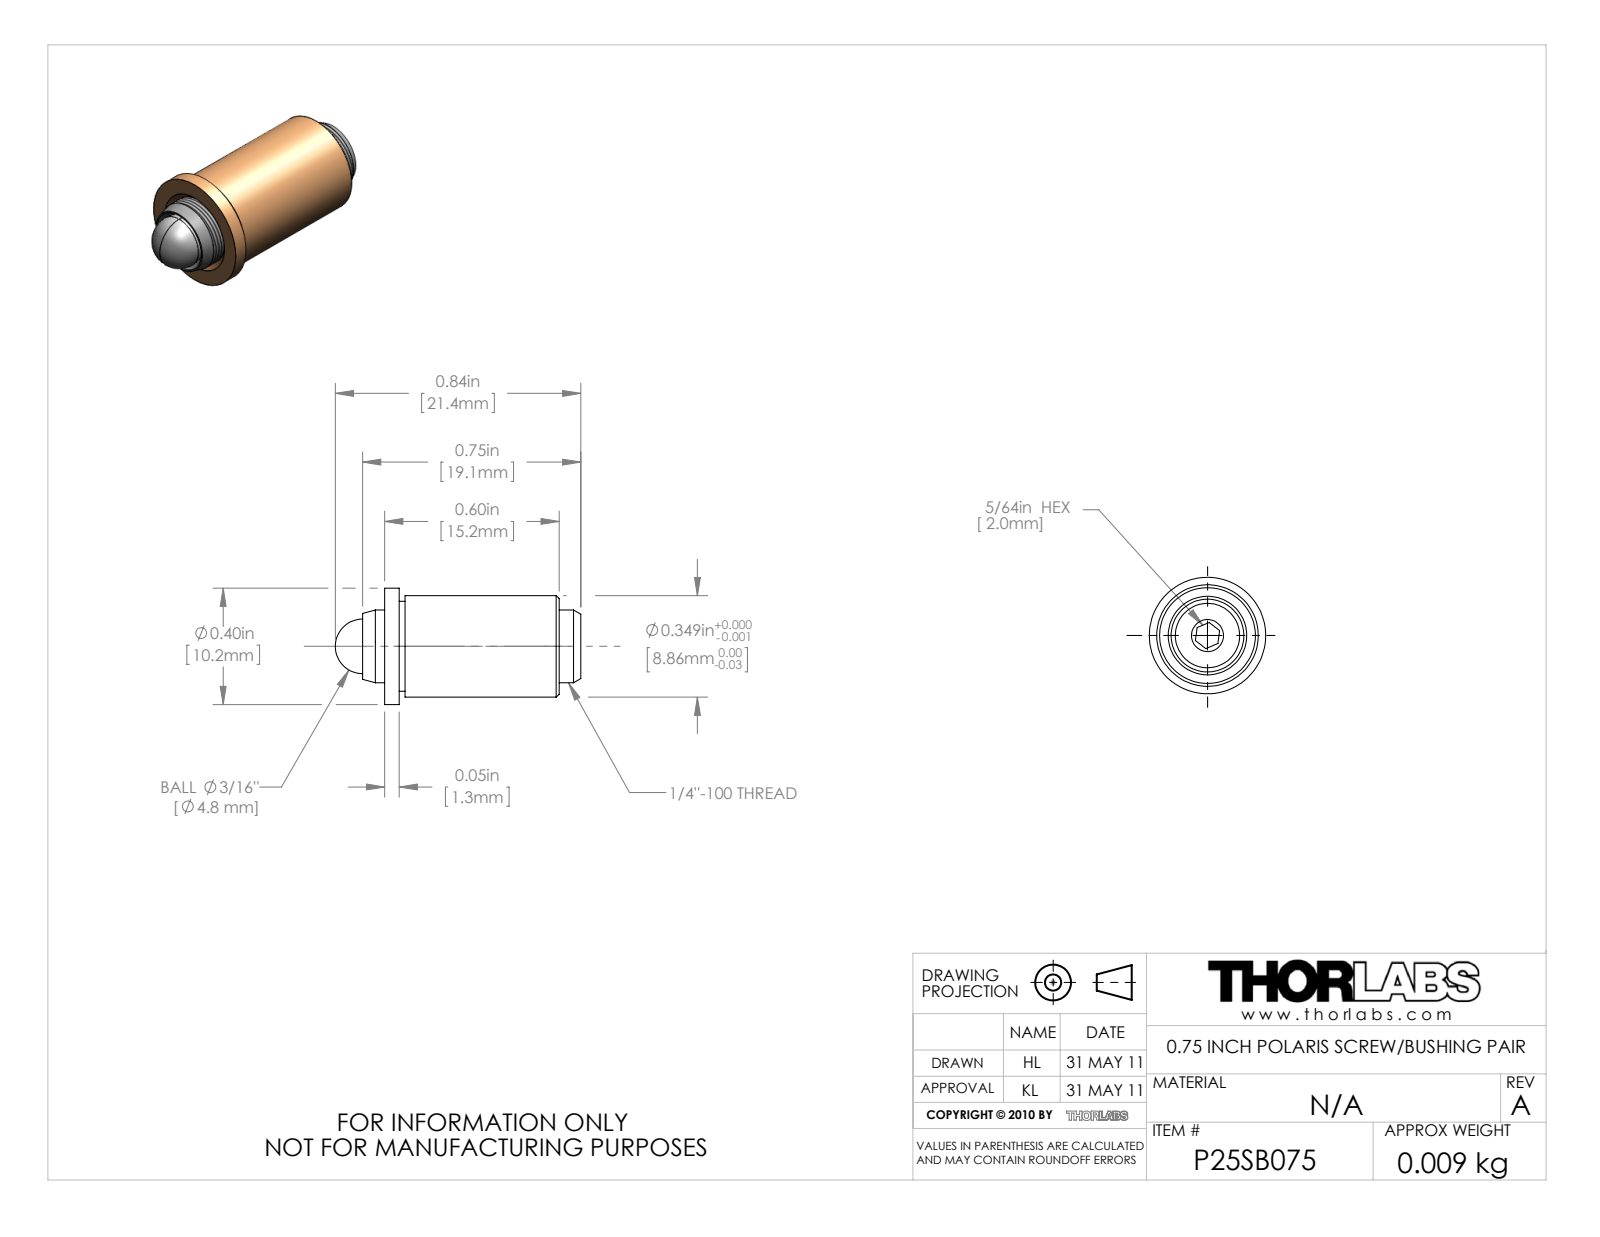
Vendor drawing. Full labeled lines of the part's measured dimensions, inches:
Part name (STEP PRODUCT): 22506-E0W
STEP written by: SolidWorks 2011 (CONFIG_CONTROL_DESIGN)
Units: inches
Bodies: 3 solids, 48 faces (18 planar, 10 cylindrical, 20 other)
Overall size (bounding box): 0.844 × 0.4 × 0.4
Volume: 0.066 in³ · Surface area: 2.161 in²
Round holes (diameter × count): ⌀0.25 ×1
Round bosses / shafts (diameter × count): ⌀0.4 ×1, ⌀0.349 ×1, ⌀0.309 ×1
Main face-to-face distances: 0.05, 0.674, 0.624, 0.6, 0.55, 0.074, 0.07, 0.02, 0.53, 0.604
